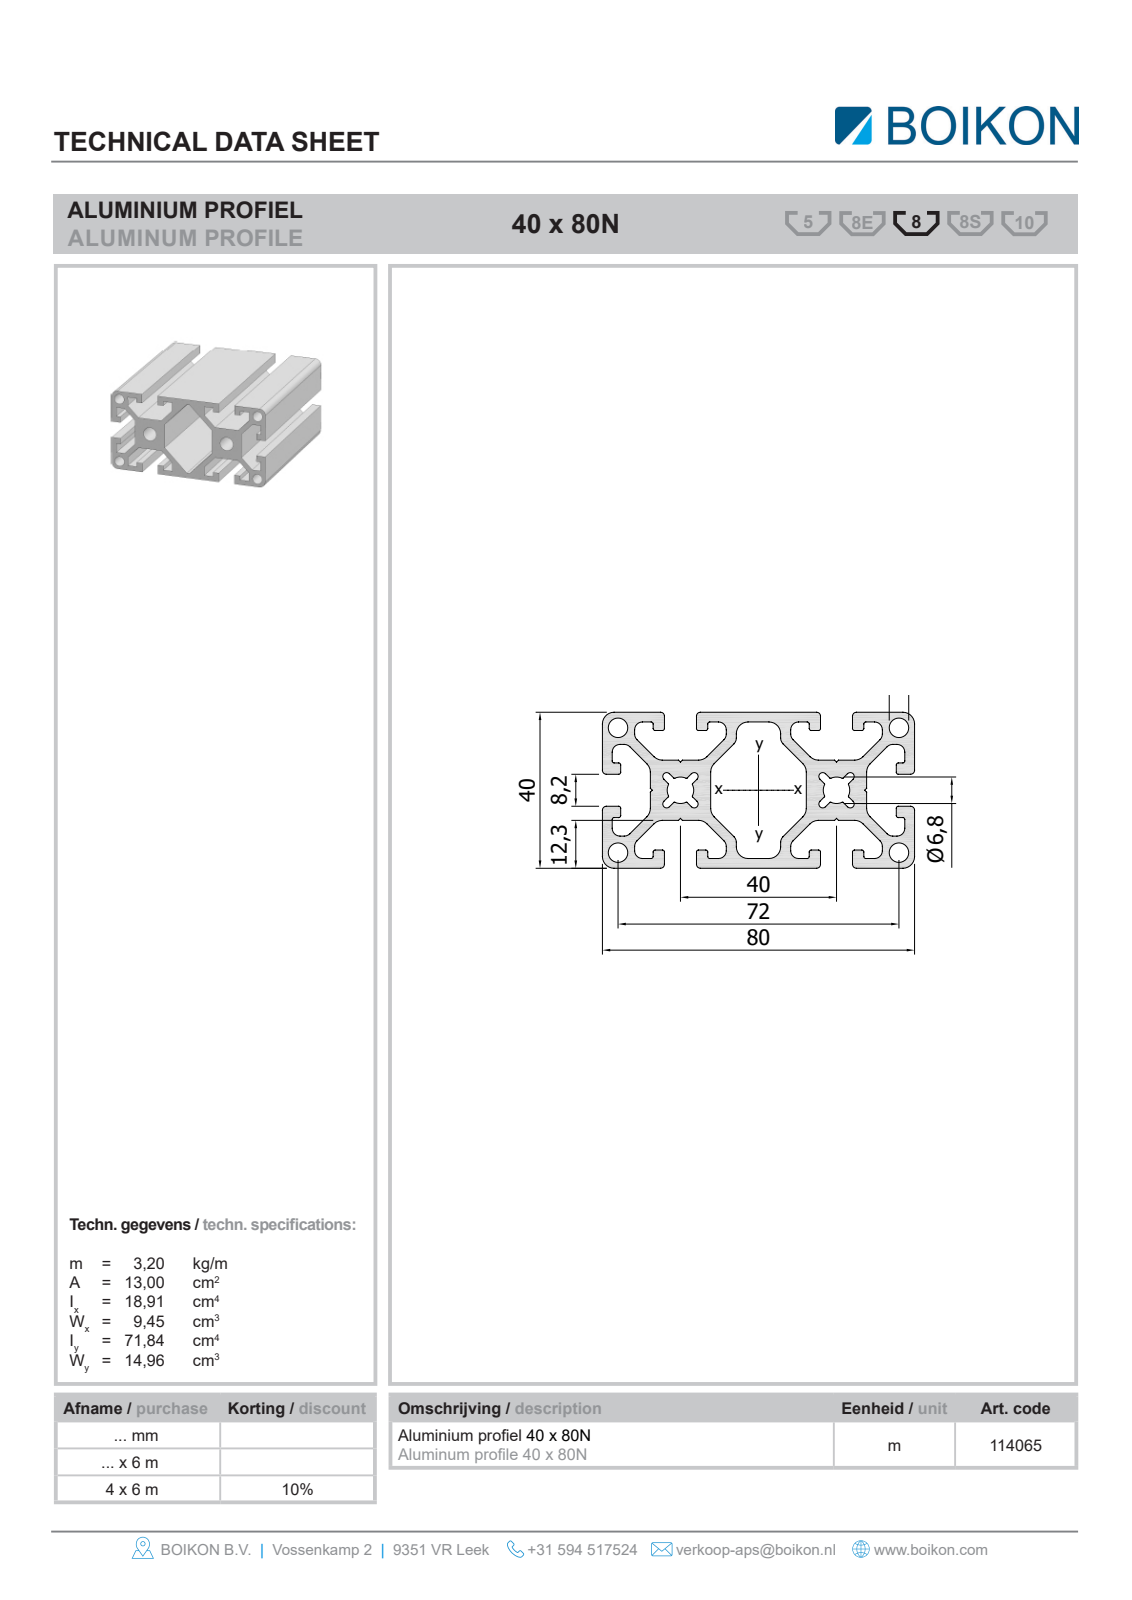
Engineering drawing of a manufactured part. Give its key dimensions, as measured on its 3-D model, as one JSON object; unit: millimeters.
{"part_name": "Root; 11406540x80NBOIKON0", "step_written_by": "HiCAD 2013 1802.4 Build 509 (AUTOMOTIVE_DESIGN)", "units": "millimeters", "bodies": {"solids": 1, "faces": 108, "planar": 98, "cylindrical": 10, "other": 0}, "overall_size": [1000, 80, 40], "volume_mm3": 1209000, "surface_area_mm2": 773907, "round_holes": [[5, 4], [6.8, 2]], "partial_cylinders_radius": [[3, 4]], "face_to_face_distances": [2.4, 40, 3.9, 12.3, 27.7, 28.28, 25.3, 23.2, 9.9, 3.6], "hole_center_spacings": [22.63, 58.24, 32, 72, 78.79, 40]}
